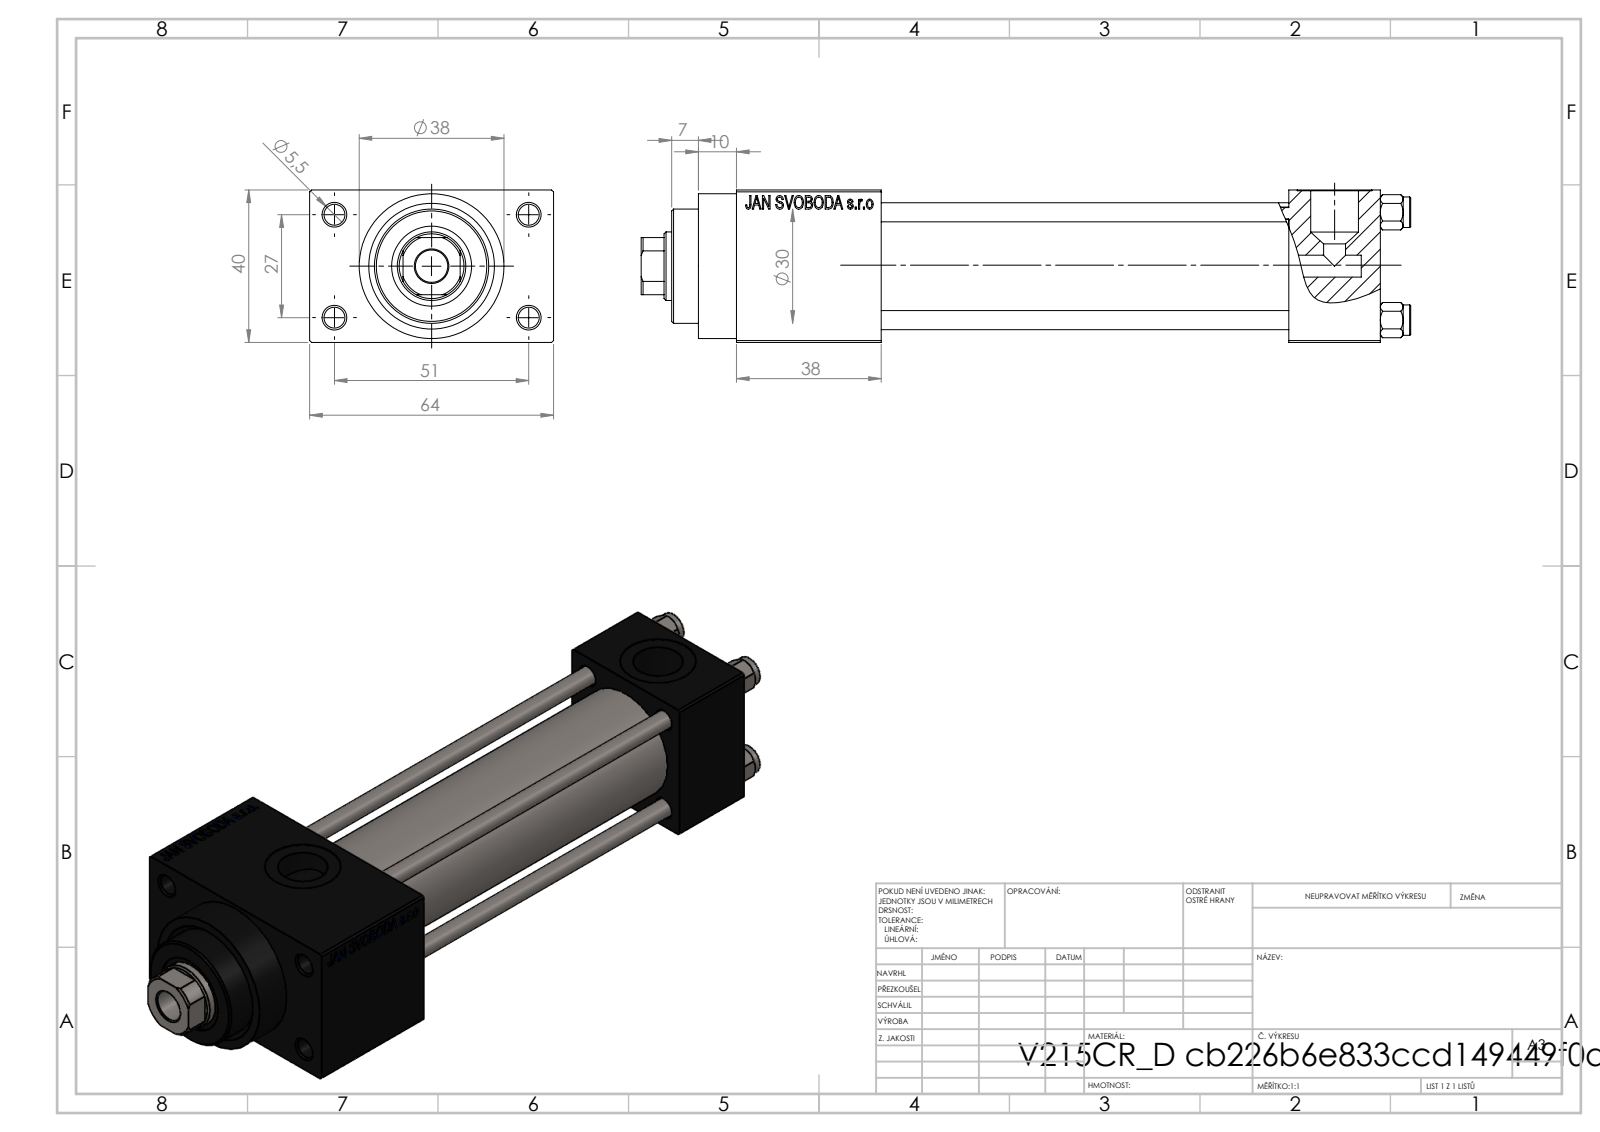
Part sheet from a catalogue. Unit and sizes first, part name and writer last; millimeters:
Units: millimetres
Overall size (bounding box): 202 × 64 × 40
Round holes (diameter × count): ⌀5 ×4, ⌀5.5 ×4, ⌀20 ×3, ⌀7 ×2, ⌀13.16 ×2, ⌀8.5 ×1, ⌀18 ×1, ⌀21 ×1, ⌀25 ×1, ⌀30 ×1
Round bosses / shafts (diameter × count): ⌀8 ×4, ⌀38 ×1, ⌀31 ×1
Partial cylindrical surfaces — rounded edges, fillets, slot ends (radius × count): R8.5 ×1
Main face-to-face distances: 40, 12, 52, 107, 24, 131, 64, 38, 169, 145
Hole centre spacings: 11.37, 20.01, 28.3, 28.85, 29.89, 39.66, 48.34, 27
Volume: 216 488 mm³ · Surface area: 81 853 mm²
Bodies: 11 solids, 1102 faces (495 planar, 87 cylindrical, 520 other)
Part name (STEP PRODUCT): NUT_M5_D; V215CR_D_TYCINKA; V215CR_D_Body; V215_VC_A (+1 more)
STEP written by: SolidWorks 2019 (CONFIG_CONTROL_DESIGN)
